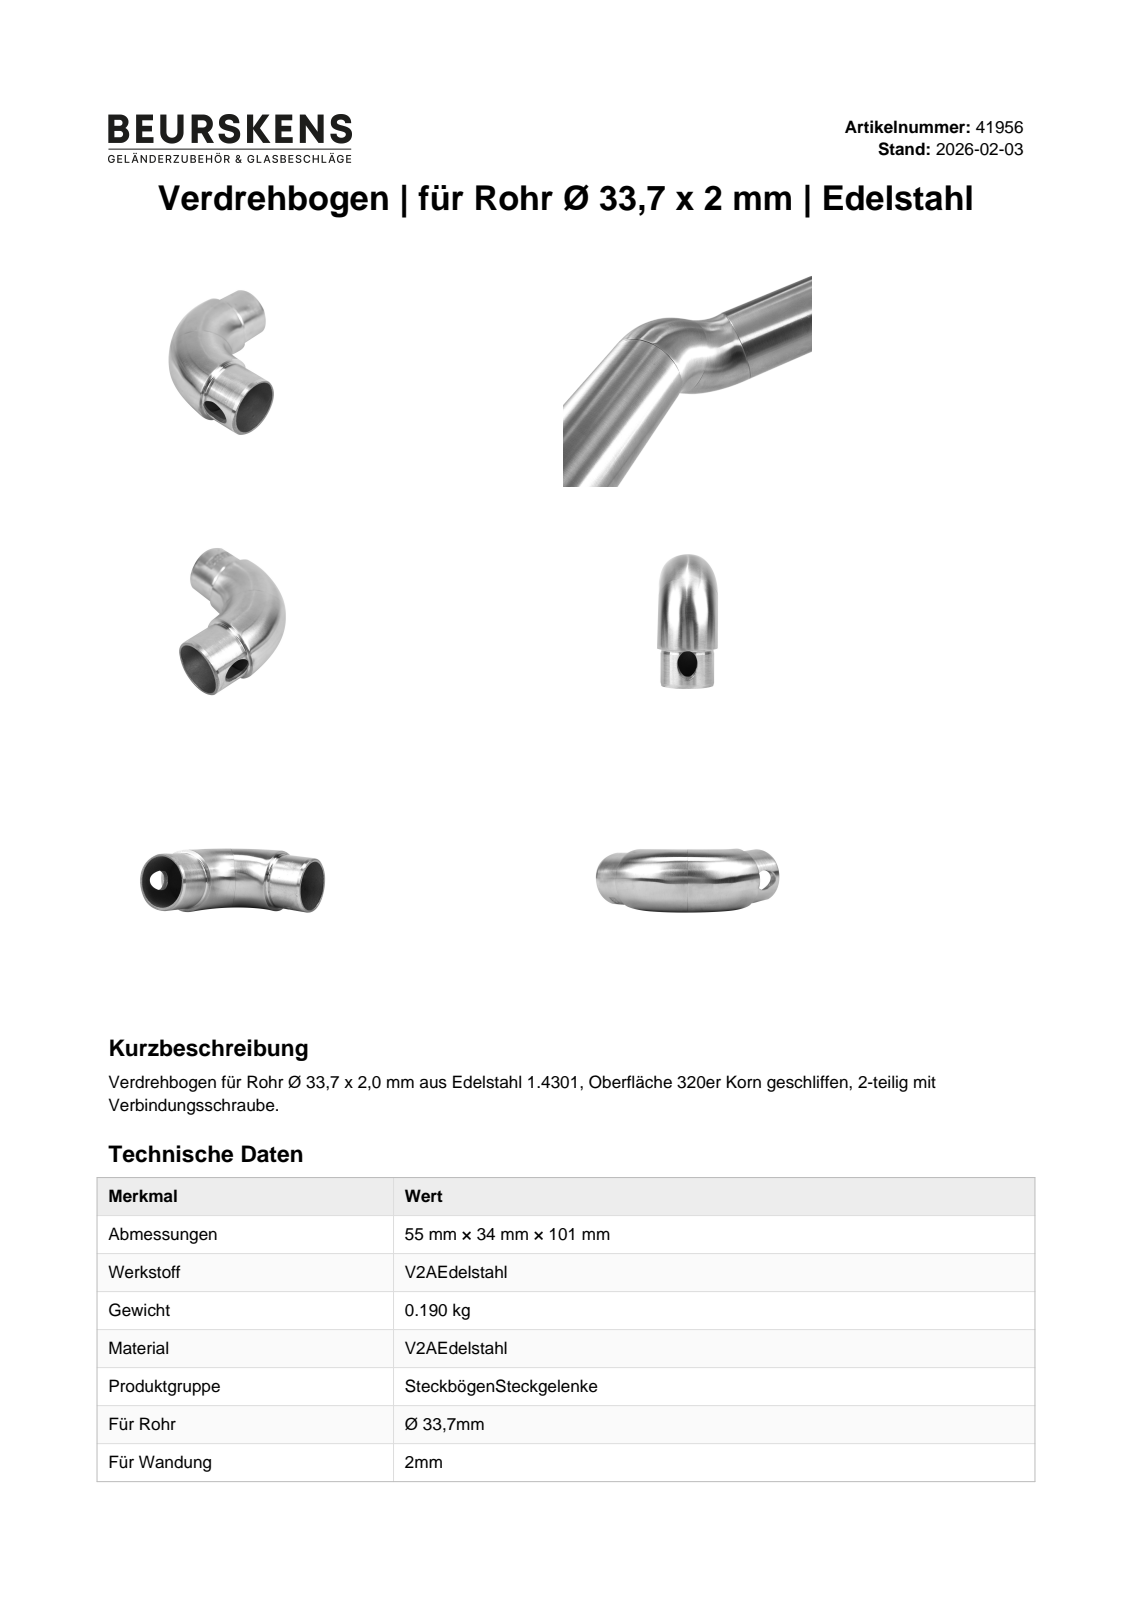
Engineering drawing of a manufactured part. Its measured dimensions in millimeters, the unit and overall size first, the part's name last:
Units: millimetres
Overall size (bounding box): 71.85 × 71.85 × 33.7
Round holes (diameter × count): ⌀25.7 ×3, ⌀8 ×1, ⌀9.5 ×1, ⌀11 ×1, ⌀29.7 ×1
Round bosses / shafts (diameter × count): ⌀29.7 ×2, ⌀13 ×1, ⌀12 ×1
Main face-to-face distances: 2, 5, 3, 4, 1, 20, 22, 7, 10.99, 8.99
Hole centre spacings: 6.82
Volume: 23 552 mm³ · Surface area: 23 474 mm²
Bodies: 3 solids, 44 faces (23 planar, 13 cylindrical, 8 other)
Part name (STEP PRODUCT): 41956; 41956-1; 41956-2; DIN 912 - M8 x 1,25 x 16 x 12,875
STEP written by: Autodesk Inventor 2022 (AUTOMOTIVE_DESIGN)
